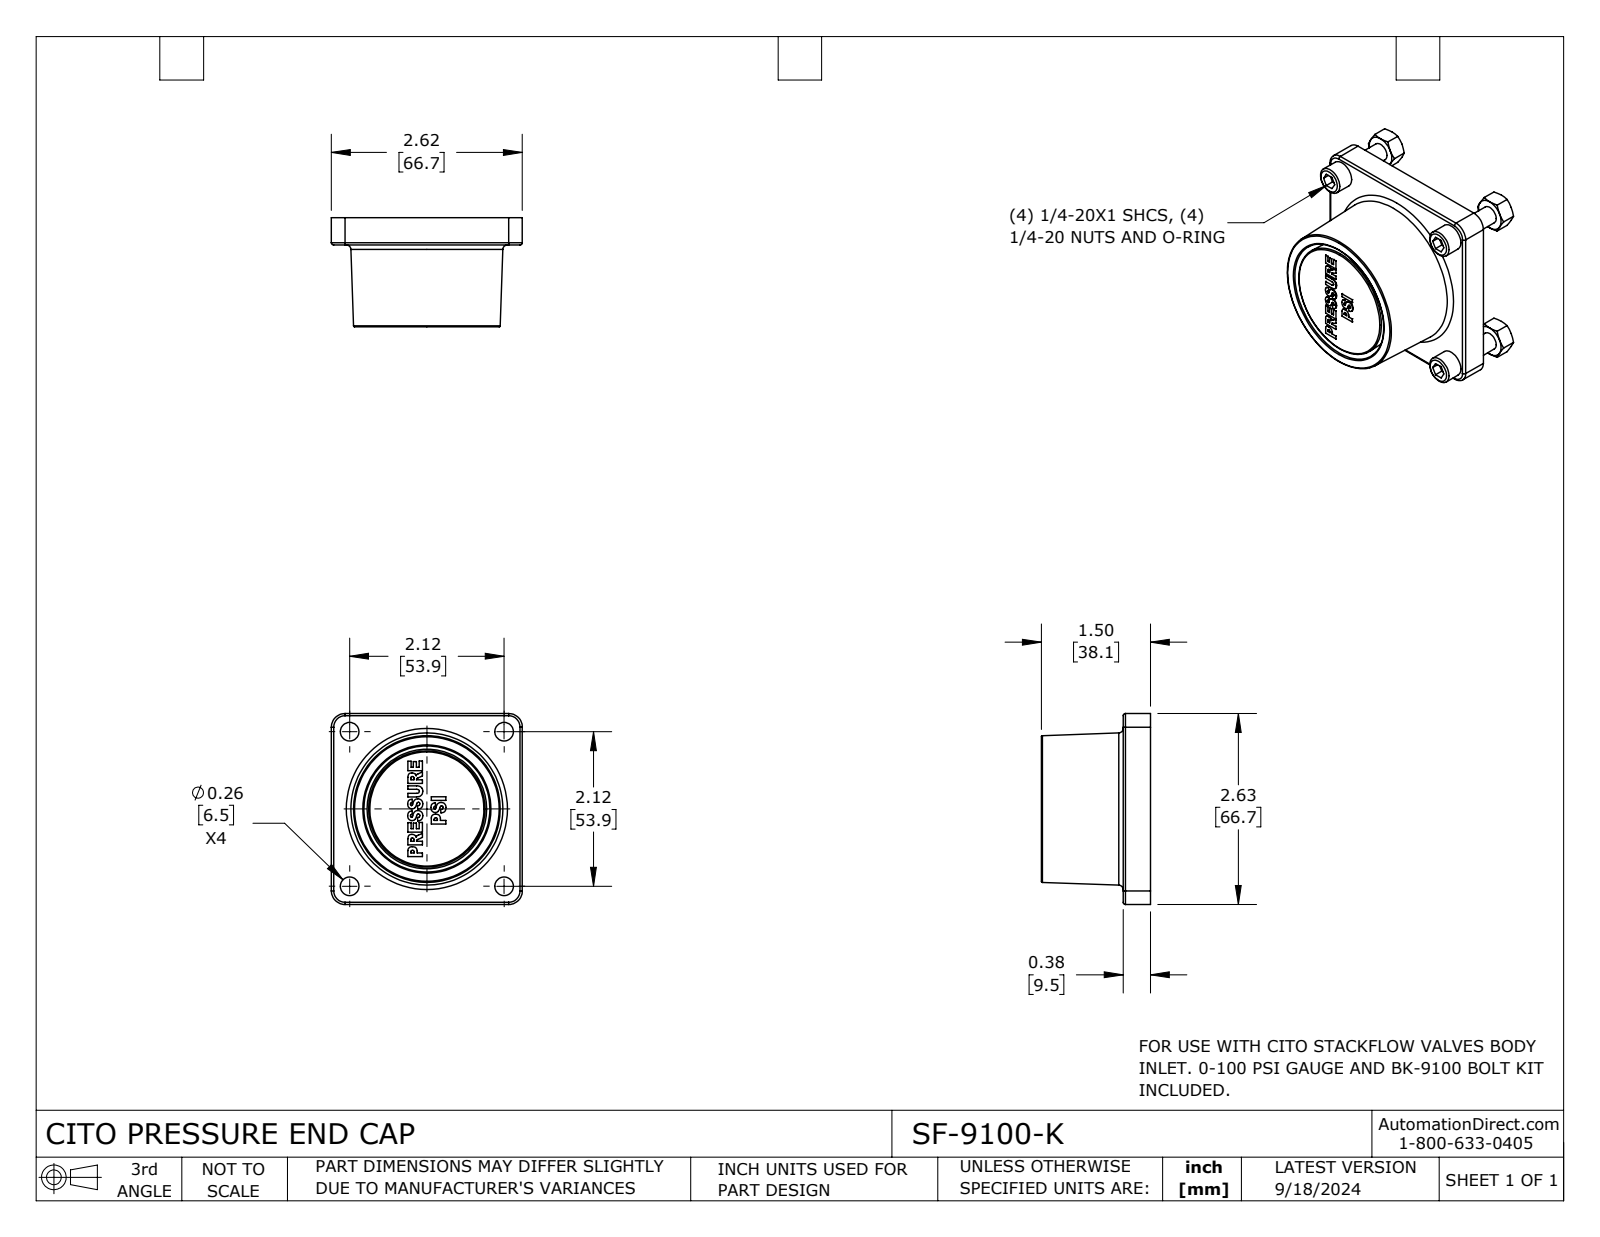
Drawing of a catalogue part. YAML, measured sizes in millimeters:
part_name: "SF-9100-K"
step_written_by: "SolidWorks 2023 (CONFIG_CONTROL_DESIGN)"
units: millimeters
bodies: {solids: 22, faces: 407, planar: 182, cylindrical: 42, other: 183}
overall_size: [66.8, 66.7, 54]
volume: 92410
surface_area: 31760
round_holes:
  - {diameter: 4.6, count: 4}
  - {diameter: 6.5, count: 4}
  - {diameter: 9.5, count: 1}
round_bosses_or_shafts:
  - {diameter: 6.4, count: 4}
  - {diameter: 9.5, count: 2}
  - {diameter: 9.5, count: 2}
partial_cylinders:
  - {radius: 0.8, count: 4}
  - {radius: 4.7, count: 2}
  - {radius: 4.8, count: 2}
face_to_face_distances: [9.5, 25.4, 28.2, 5.1, 4.4, 37.7, 32.6, 12.3, 7.2, 2.8]
hole_center_spacings: [38.2, 53.9, 76.3]
